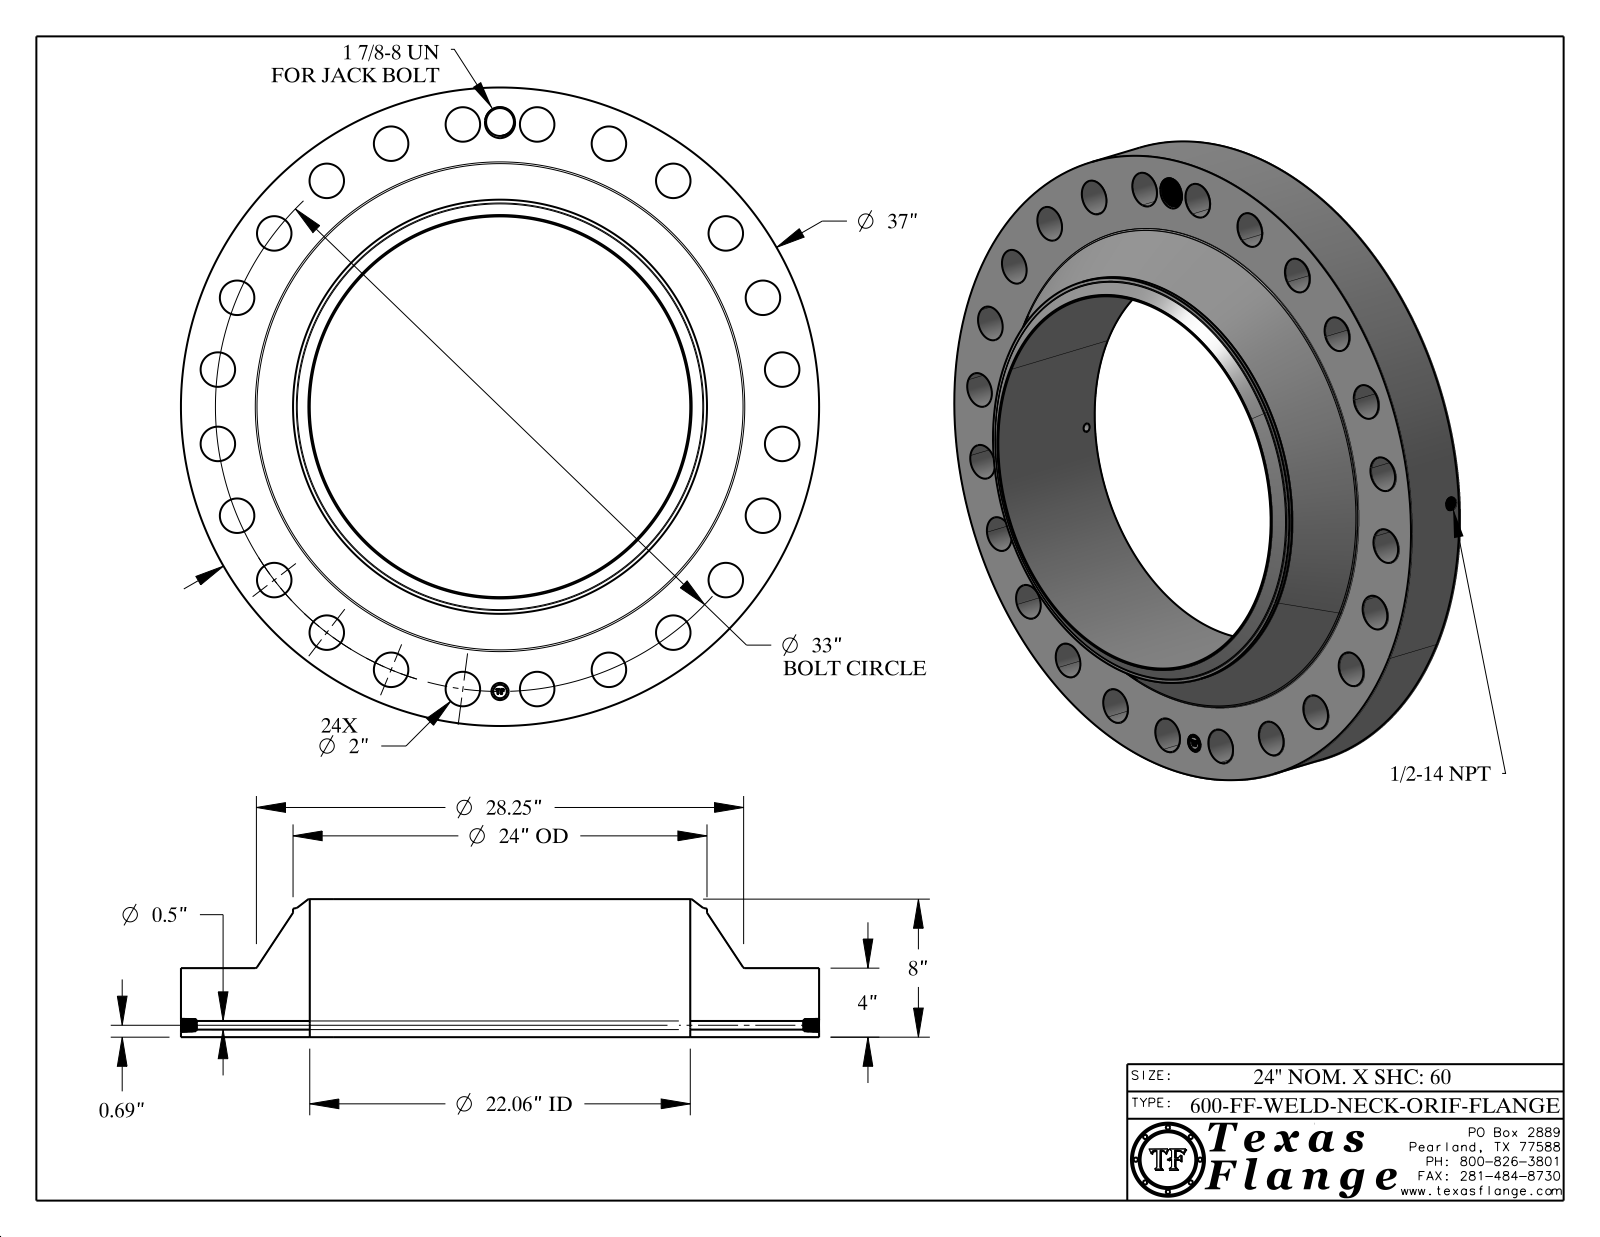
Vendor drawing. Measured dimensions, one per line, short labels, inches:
name: 600-FF-WELD-NECK
written by: CATIA V5 STEP AP214 (AUTOMOTIVE_DESIGN)
unit: in
bodies: 1 solid, 904 faces (368 planar, 157 cylindrical, 379 other)
size: 37 × 37 × 8
volume: 2 989 in³; area: 3 102 in²
holes: 24× ⌀2, 1× ⌀0.5, 1× ⌀0.672, 1× ⌀1, 1× ⌀1.615, 1× ⌀22.062
bosses: 8× ⌀0.061, 1× ⌀37, 1× ⌀24, 1× ⌀0.788
face distances: 4, 8, 3.985, 0.015, 4.015, 0.298, 0.293, 0.054, 0.248, 0.193
hole spacings: 16.5, 8.541, 20.089, 28.579, 12.628, 4.307, 23.334, 26.181
